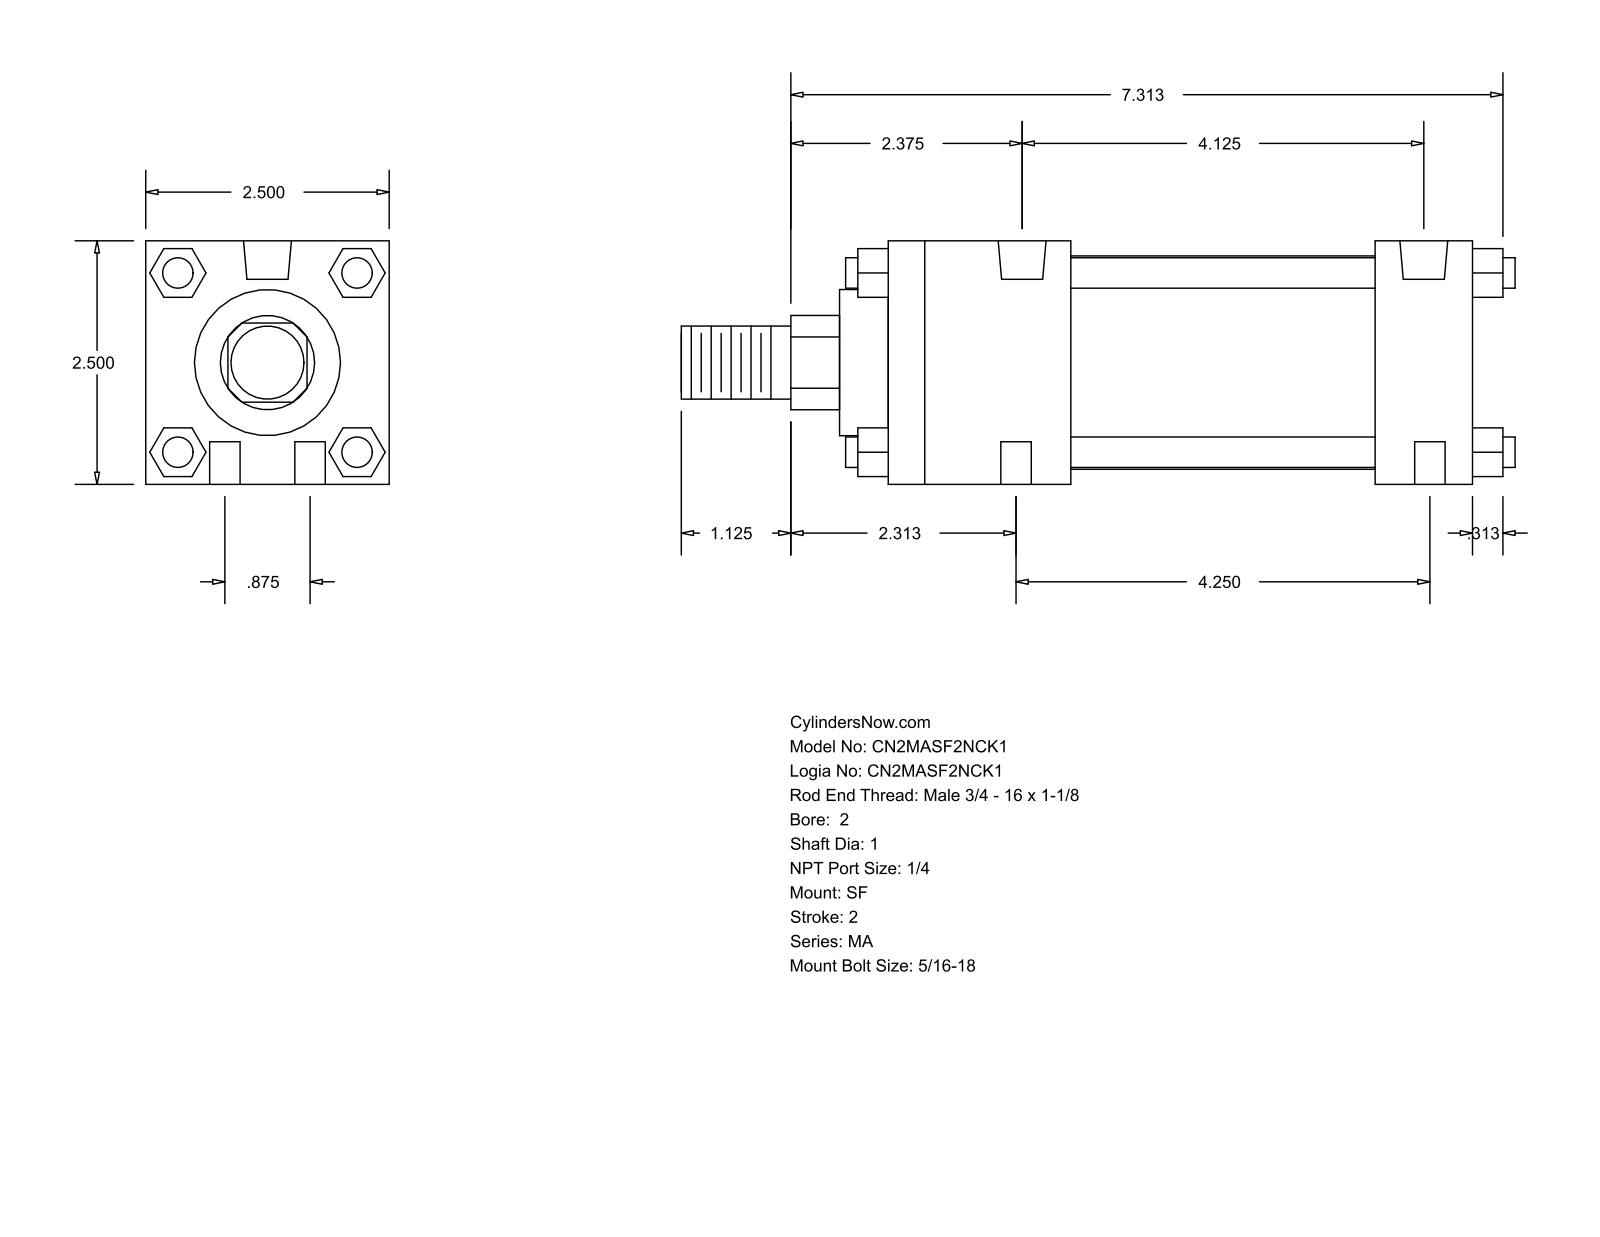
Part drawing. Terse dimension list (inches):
name: MA_SF__0200_1
written by: GSSL Pune (CONFIG_CONTROL_DESIGN)
unit: in
bodies: 0 solids, 124 faces (94 planar, 30 cylindrical, 0 other)
size: 8.563 × 2.5 × 2.5
holes: 6× ⌀0.313, 2× ⌀0.492
bosses: 4× ⌀0.313, 1× ⌀2.19, 1× ⌀1.5, 1× ⌀1, 1× ⌀0.75
rounds: 1× R0.484
face distances: 2.5, 6, 0.5, 1, 5, 1.875, 3.125, 4.125, 0.92, 1.593
hole spacings: 0.442, 4.21, 0.875, 4.125, 4.25, 4.339
